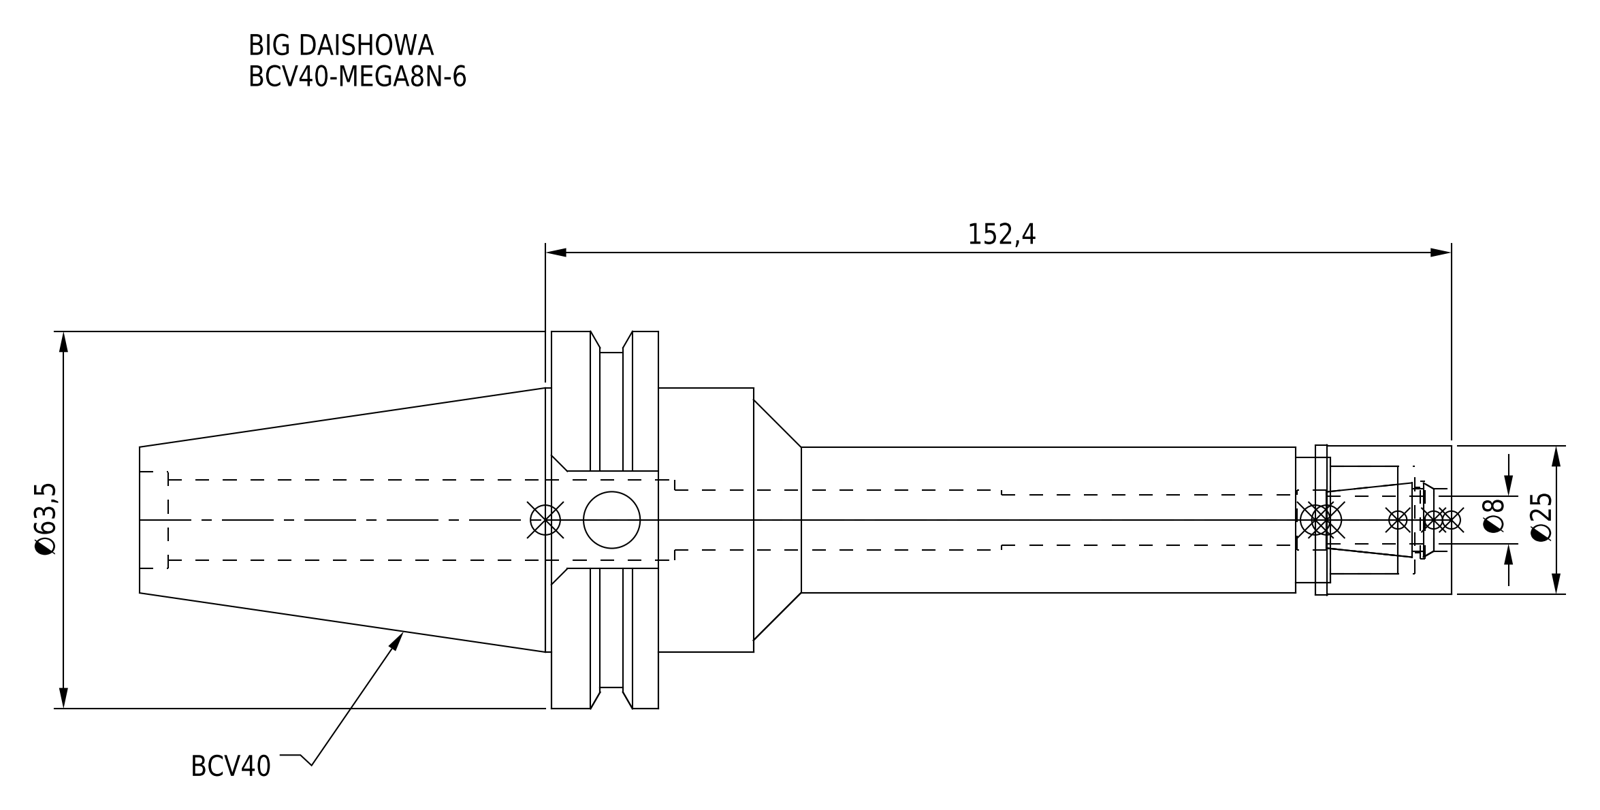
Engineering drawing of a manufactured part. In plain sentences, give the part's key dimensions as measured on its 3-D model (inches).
The part is named "BCV40-MEGA8N-6_1.stp; DXF_TEMP_ASSY_ASM_4_ASM.stp; BCV40-MEGA8N-6-080-FreeParts; BCV40-MEGA8N-6-080.stp (+3 more)". Its 3-D file was written by "SolidWorks 2019 (CONFIG_CONTROL_DESIGN)". It is 2 solids with 91 faces: 33 planar, 44 cylindrical and 14 other. Overall it measures 8.687 by 2.5 by 2.415 inches. Its volume is 10.78 cubic inches and its surface area 59.19 square inches. Round holes: 1 of diameter 0.331, 1 of diameter 0.375, 1 of diameter 0.394, 1 of diameter 0.413, 1 of diameter 0.433, 1 of diameter 0.512, 1 of diameter 0.535, 1 of diameter 0.643, 1 of diameter 0.709, 1 of diameter 0.827. Round bosses or shafts: 1 of diameter 2.5, 1 of diameter 2.219, 1 of diameter 1.75, 1 of diameter 0.996, 1 of diameter 0.984, 1 of diameter 0.965. The main face-to-face distances are 0.711, 5.25, 5.961, 8.687, 3.437, 2.726, 4.622, 0.628, 1.339, 4.065.
